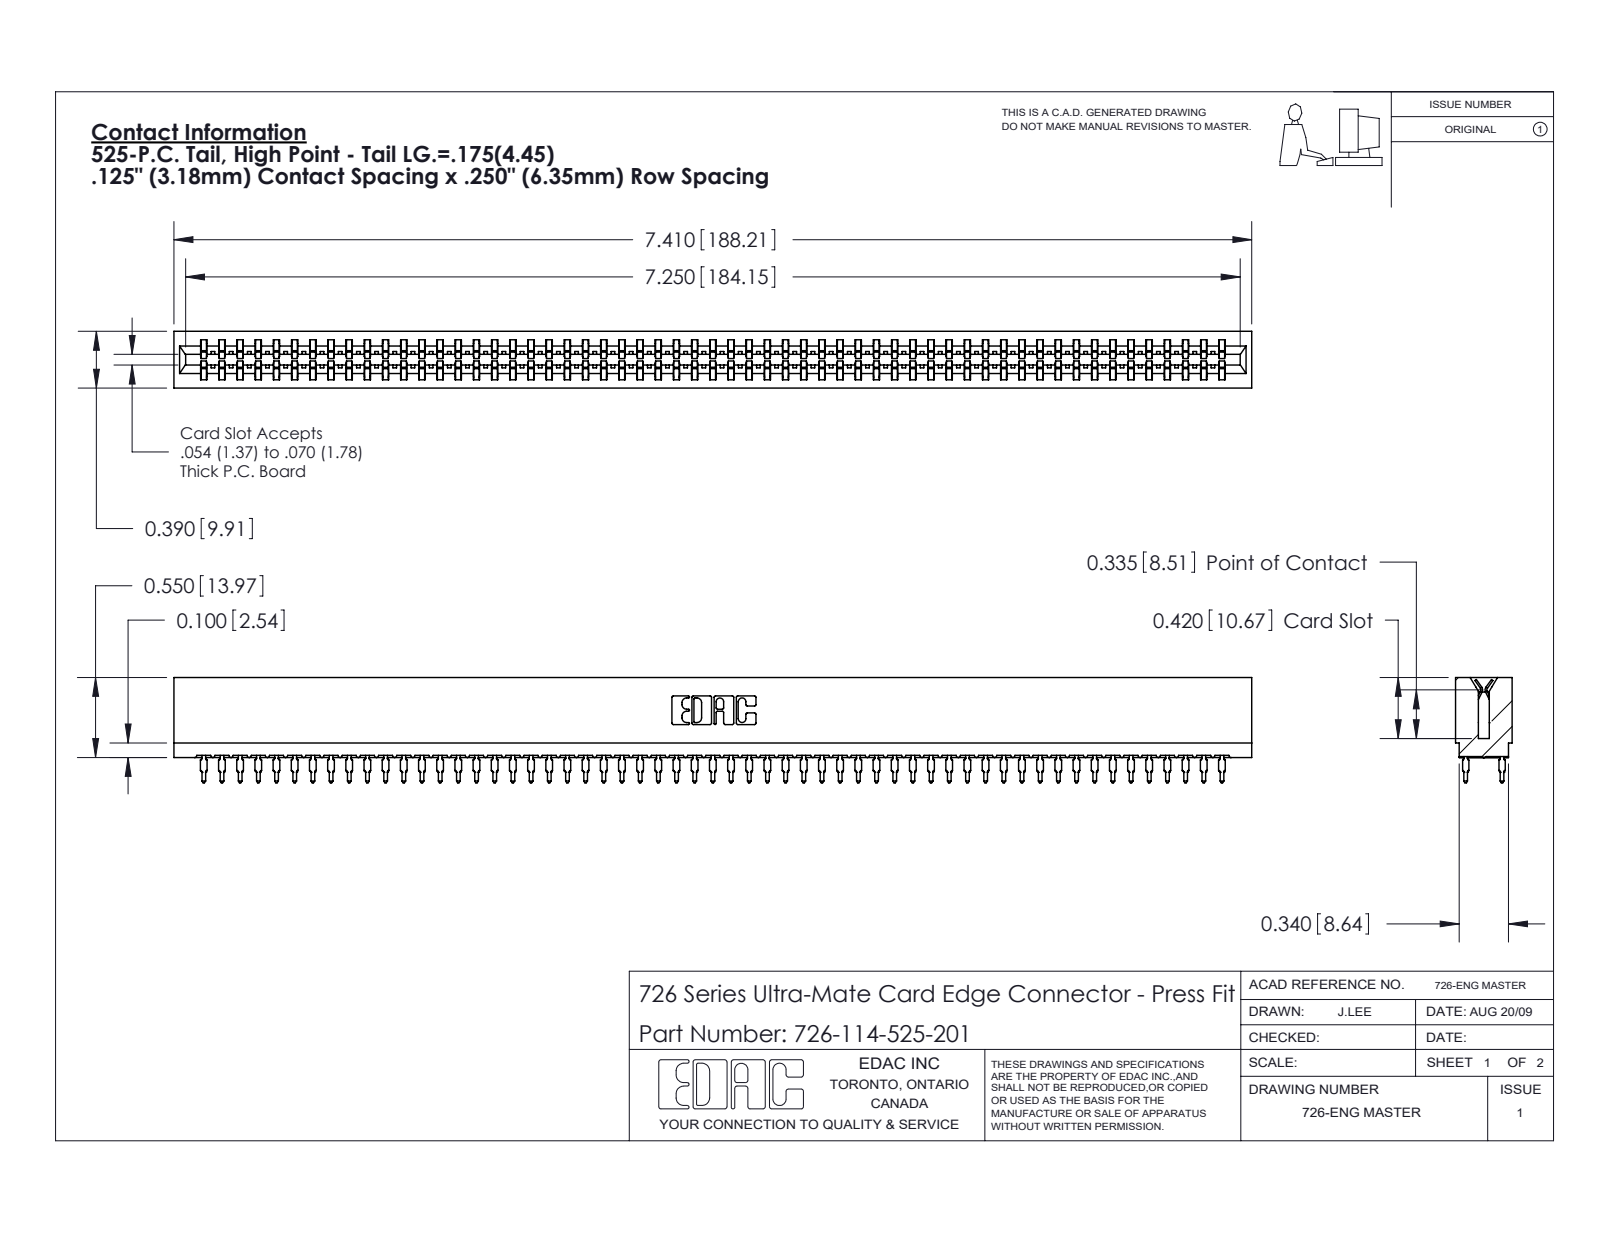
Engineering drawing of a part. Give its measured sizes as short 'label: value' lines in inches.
name: 746-292-001_525; 726 Part_.515 Slot Depth - 01; 726-114-525-201
written by: SolidWorks 2020 (CONFIG_CONTROL_DESIGN)
unit: in
bodies: 115 solids, 10300 faces (5299 planar, 2037 cylindrical, 2964 other)
size: 7.41 × 0.724 × 0.39
volume: 1.049 in³; area: 44.39 in²
rounds: 228× R0.021, 58× R0.015, 22× R0.01, 8× R0.005, 8× R0.011, 6× R0.007, 6× R0.031, 3× R0.026
face distances: 0.057, 0.333, 0.39, 0.025, 0.307, 0.25, 0.275, 0.083, 0.365, 0.032
